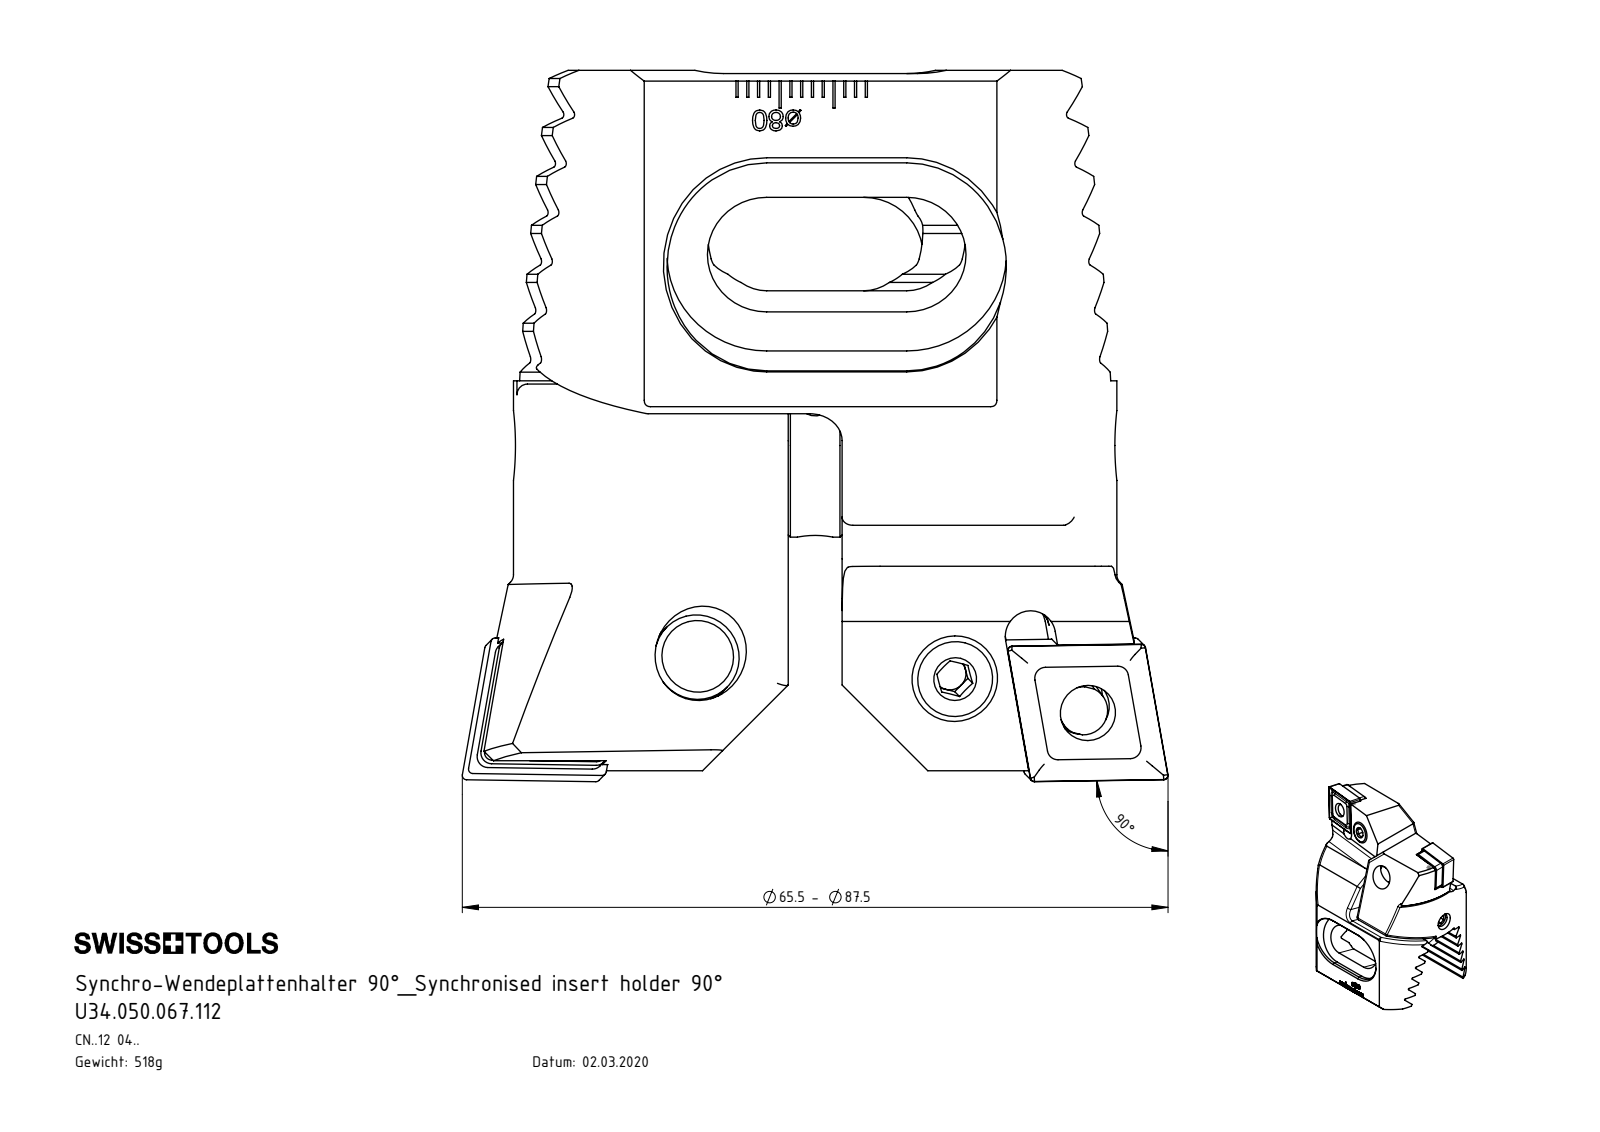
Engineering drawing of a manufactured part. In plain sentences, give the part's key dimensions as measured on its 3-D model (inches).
The part is named "WCD-ER3.101.000_A; WCD-ER4.101.017_A; Z55-xxx.001.037_C_CN12; Z55.WCD.B12.037 (+8 more)". Its 3-D file was written by "SolidWorks 2017 (AUTOMOTIVE_DESIGN)". It is 17 solids with 817 faces: 445 planar, 135 cylindrical and 237 other. Overall it measures 2.598 by 2.579 by 1.74 inches. Its volume is 3.93 cubic inches and its surface area 42.63 square inches. Round holes: 3 of diameter 0.13, 2 of diameter 0.079, 2 of diameter 0.203, 2 of diameter 0.252, 2 of diameter 0.276, 2 of diameter 0.331, 1 of diameter 0.197. Round bosses or shafts: 3 of diameter 0.157, 2 of diameter 0.315, 2 of diameter 0.311, 2 of diameter 0.252, 2 of diameter 0.177, 2 of diameter 0.14, 1 of diameter 0.669, 1 of diameter 0.236. Partial cylindrical surfaces (rounded edges, fillets, slot ends): 22 of radius 0.039, 12 of radius 0.013, 8 of radius 0.016, 6 of radius 0.098, 6 of radius 0.118, 4 of radius 0.217, 4 of radius 0.364, 4 of radius 0.472. The main face-to-face distances are 0.16, 0.32, 0.481, 0.641, 0.801, 0.197, 0.309, 0.067, 0.02, 1.74. The hole center spacings are 0.504, 0.506, 0.63, 1.217.
